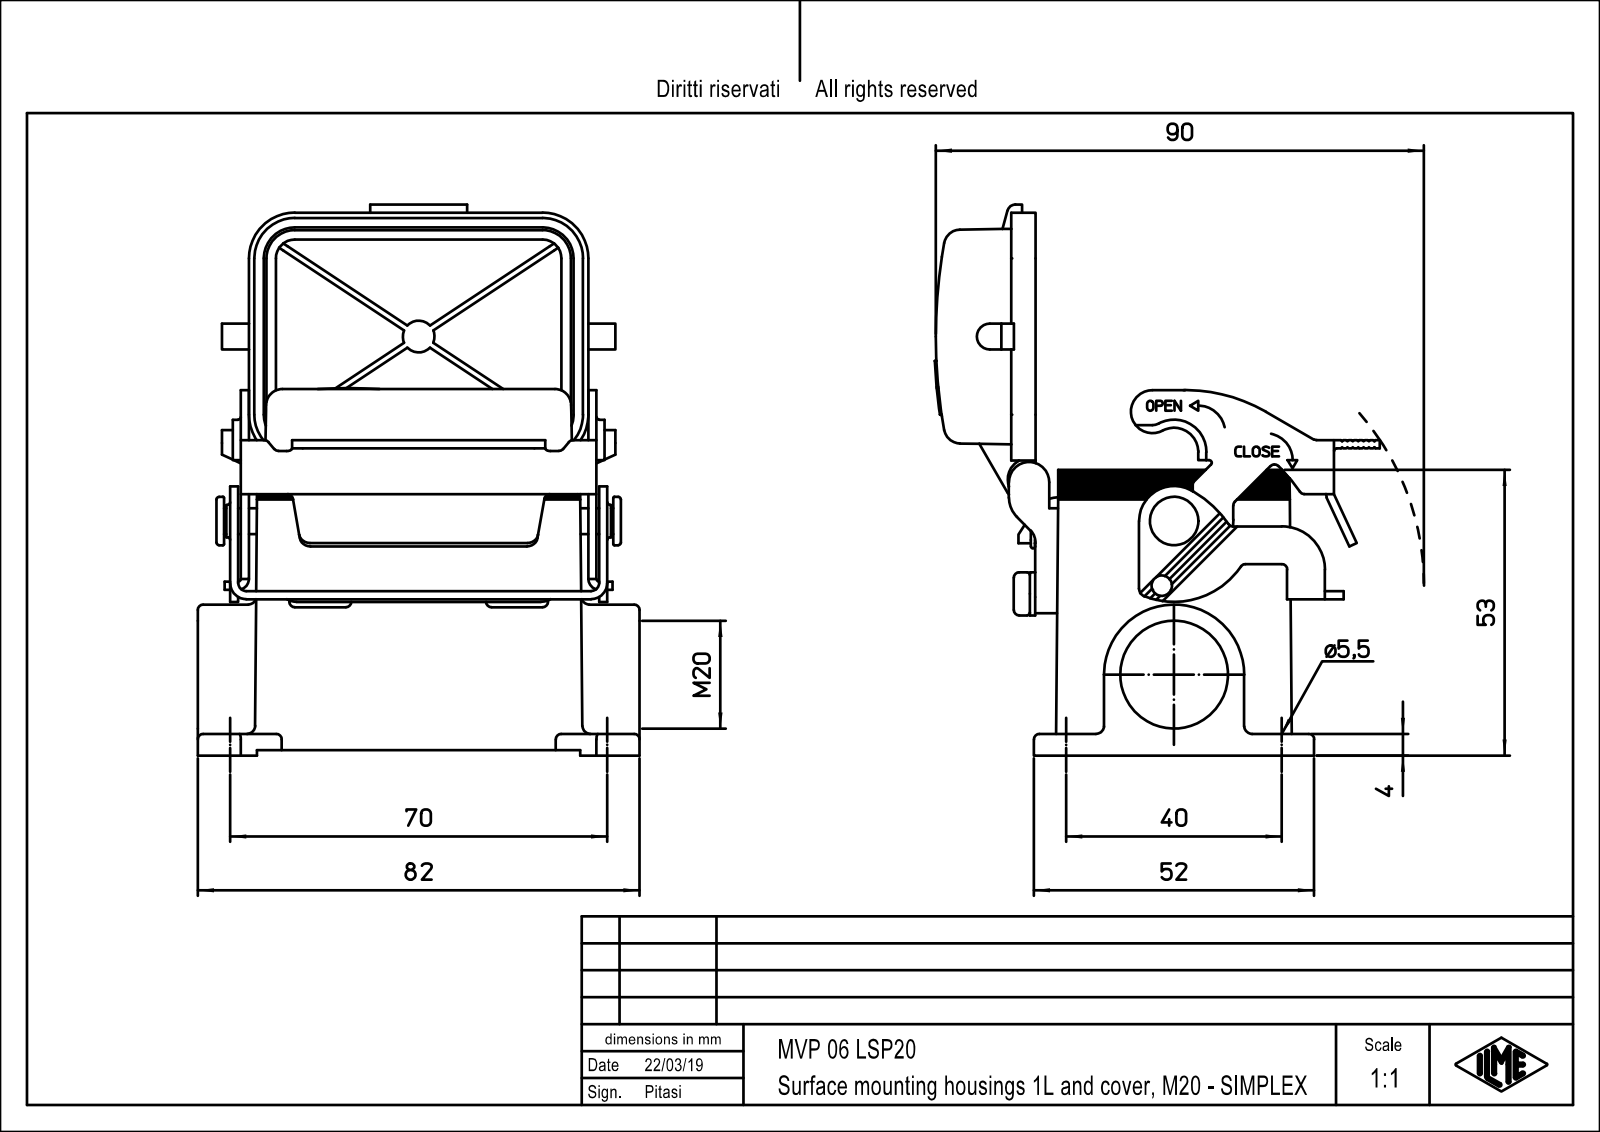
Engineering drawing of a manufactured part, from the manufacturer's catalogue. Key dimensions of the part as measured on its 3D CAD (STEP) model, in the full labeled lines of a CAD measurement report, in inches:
Part name (STEP PRODUCT): MVP_06_LSP20.stp
STEP written by: PTC Creo Elements/Direct Modeling 19.0E 27-Jun-2016 (C) Parametric Technology GmbH (AUTOMOTIVE_DESIGN)
Units: inches
Bodies: 1 solid, 607 faces (384 planar, 199 cylindrical, 24 other)
Overall size (bounding box): 4.044 × 3.228 × 3.138
Volume: 5.471 in³ · Surface area: 82.57 in²
Round holes (diameter × count): ⌀0.097 ×4, ⌀0.118 ×4, ⌀0.217 ×4, ⌀0.597 ×1, ⌀0.787 ×1, ⌀0.833 ×1
Round bosses / shafts (diameter × count): ⌀0.031 ×3, ⌀0.354 ×1, ⌀0.331 ×1, ⌀0.315 ×1, ⌀0.236 ×1, ⌀0.197 ×1, ⌀0.094 ×1
Partial cylindrical surfaces — rounded edges, fillets, slot ends (radius × count): R0.079 ×18, R0.118 ×11, R0.059 ×8, R0.138 ×7, R0.039 ×5, R0.236 ×5, R0.02 ×4, R0.071 ×4
Main face-to-face distances: 0.157, 1.594, 0.059, 1.88, 0.079, 0.315, 1.752, 1.437, 0.571, 2.343
Hole centre spacings: 0.572, 1.415, 2.259, 2.603, 1.063, 1.575, 1.732, 2.032
